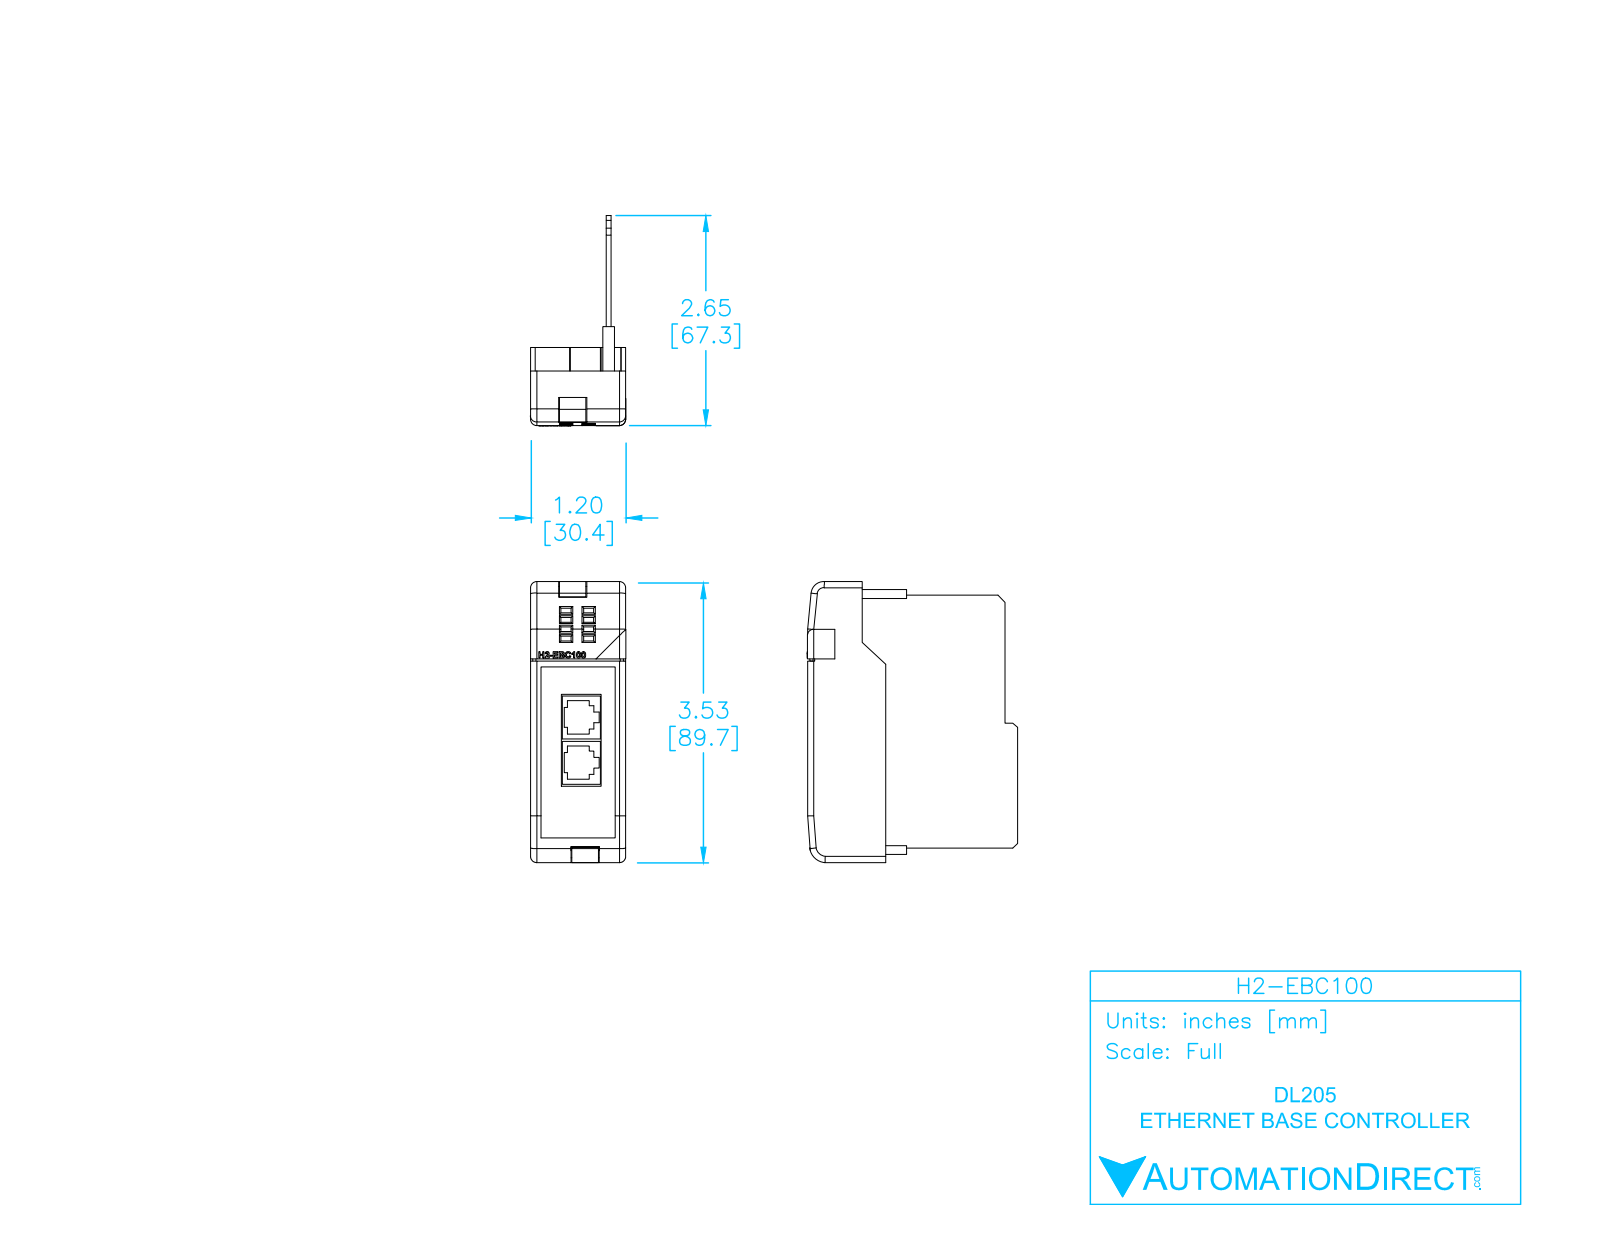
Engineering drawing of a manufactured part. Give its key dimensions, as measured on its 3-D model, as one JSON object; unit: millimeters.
{"part_name": "H2-EBC100", "step_written_by": "SolidWorks 2009 (AUTOMOTIVE_DESIGN)", "units": "millimeters", "bodies": {"solids": 4, "faces": 431, "planar": 280, "cylindrical": 84, "other": 67}, "overall_size": [90, 67.38, 30.55], "volume_mm3": 19329, "surface_area_mm2": 29786, "partial_cylinders_radius": [[0.5, 28], [2, 11], [0.25, 4], [1, 2], [2.62, 1], [3.79, 1], [4.12, 1], [5.29, 1]], "face_to_face_distances": [1.5, 4.72, 3.22, 6.22, 24.28, 29, 0.5, 25.78, 30.5, 22.78]}
